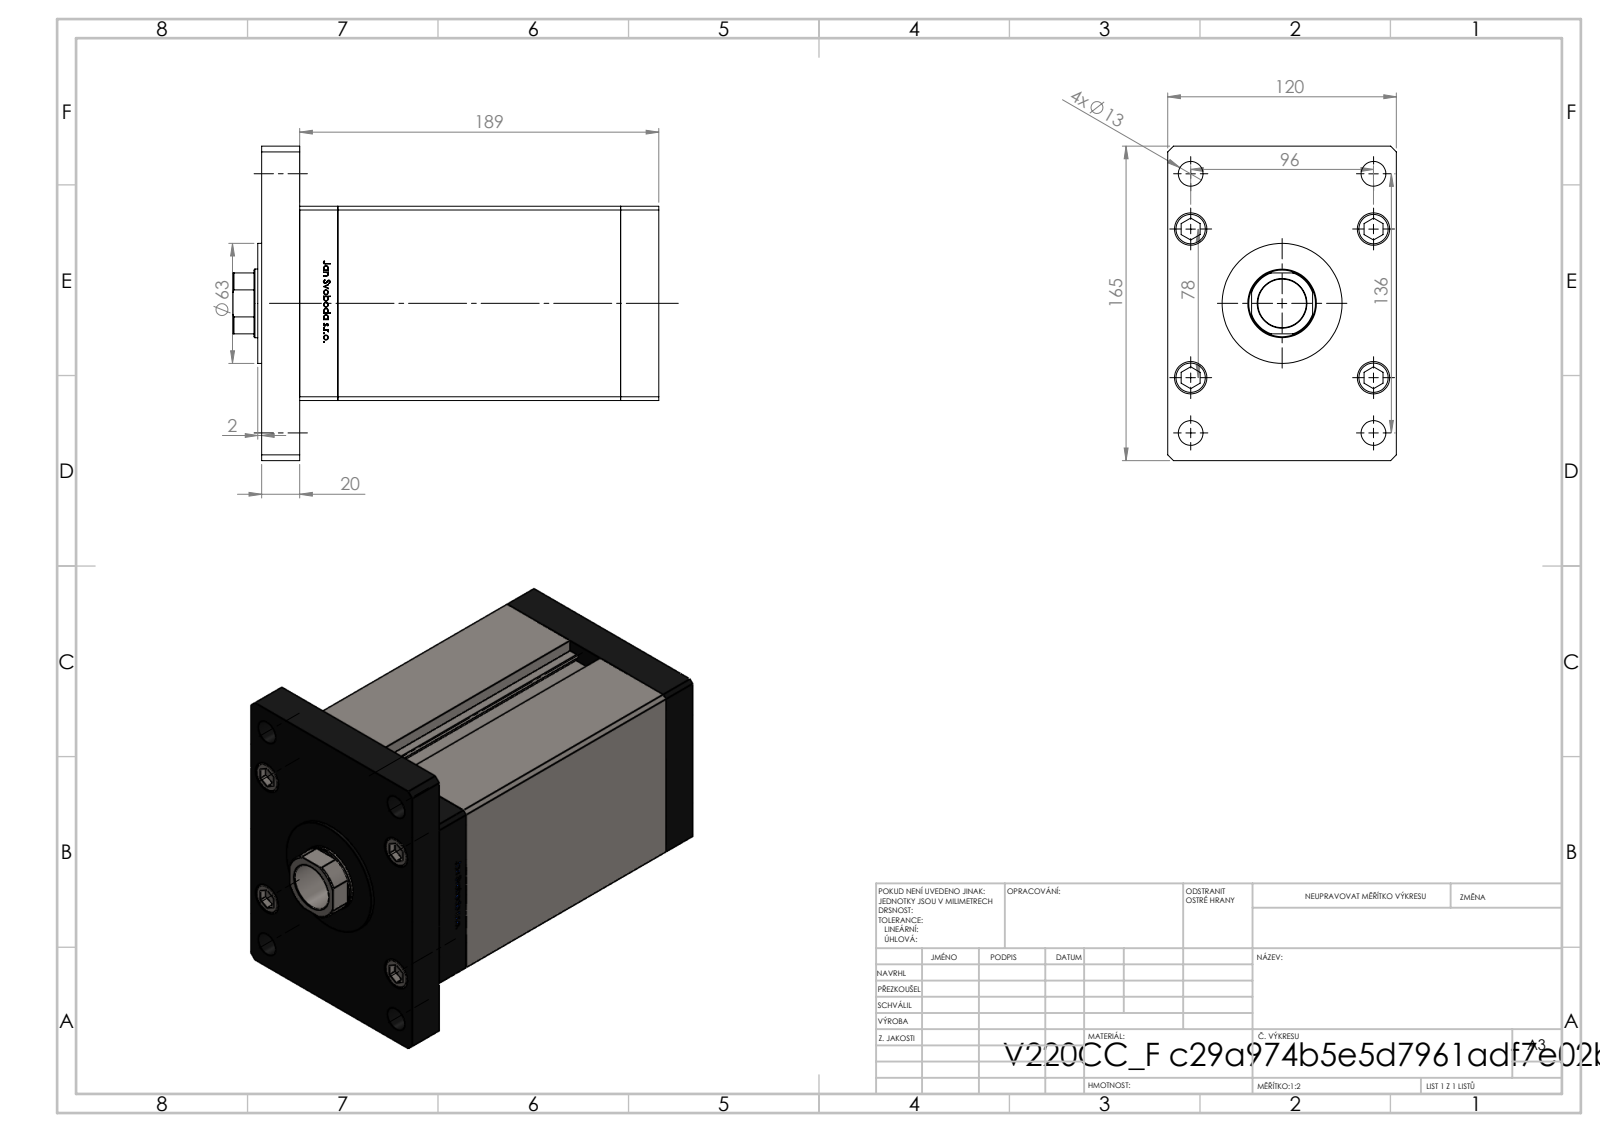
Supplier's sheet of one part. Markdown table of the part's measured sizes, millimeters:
| quantity | value |
| --- | --- |
| part name | ALLEN BOLT; V220C BACK_F; V220C_FRONT_F; V220C_VC_F (+2 more) |
| STEP written by | SolidWorks 2019 (CONFIG_CONTROL_DESIGN) |
| units | millimeters |
| bodies | 19 solids, 1311 faces (517 planar, 188 cylindrical, 606 other) |
| overall size | 223.5 × 165 × 120 |
| volume | 2 417 000 mm³ |
| surface area | 321 367 mm² |
| round holes (diameter × count) | 13.5 × 5, 18 × 5, 12 × 4, 13 × 4, 17 × 4, 2 × 2, 13.16 × 2, 25.5 × 1, 36 × 1, 37.5 × 1 |
| round bosses / shafts (diameter × count) | 8 × 9, 17 × 5, 63 × 1 |
| partial cylindrical surfaces (radius × count) | 0.93 × 2, 17.5 × 1 |
| main face-to-face distances | 20, 168.5, 188.5, 120, 102, 148.5, 40, 208.5, 34.25, 22 |
| hole center spacings | 41.5, 29, 61.85, 83.23, 96, 100.28, 107, 143.75 |
